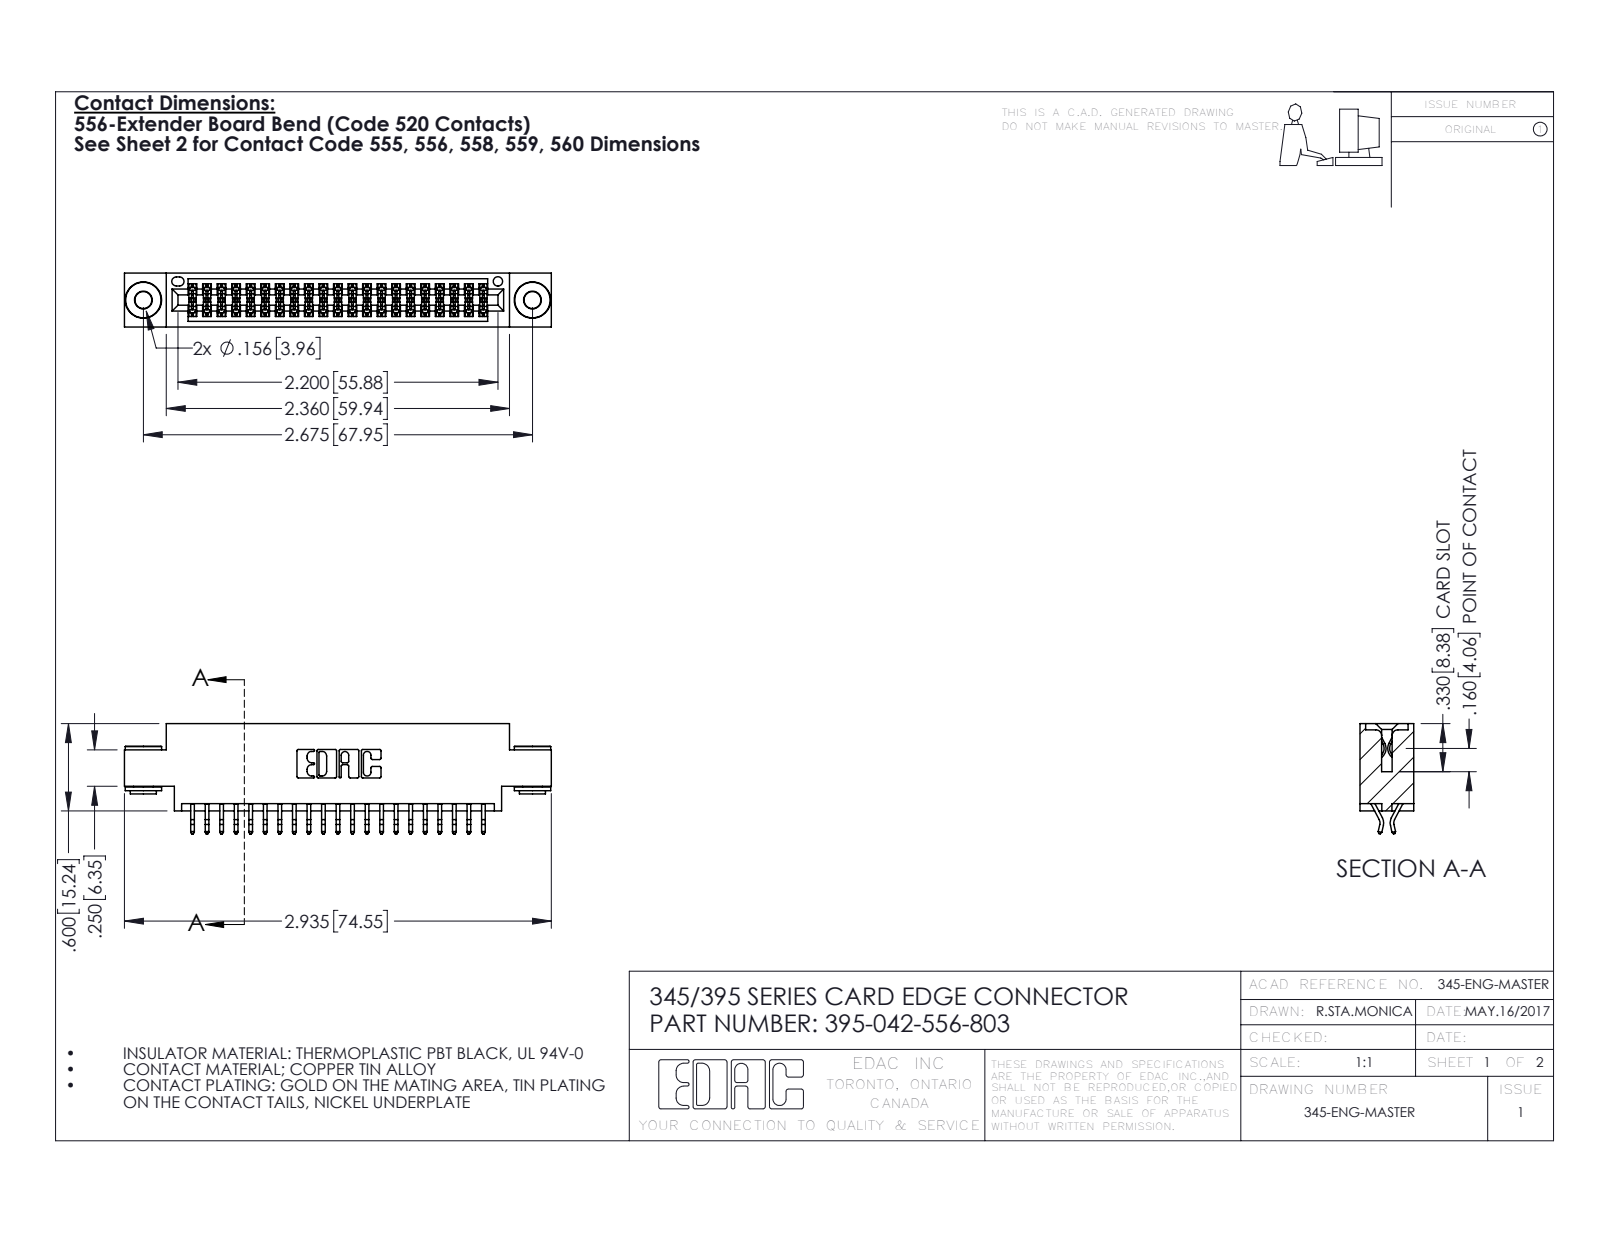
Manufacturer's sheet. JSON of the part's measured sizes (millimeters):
{"part_name": "345-292-001_556 Tail; 345 Part_0.170 Offset - 0.156 Dia-TH; 395-042-556-803; 345-250-002_345-250-002-102", "step_written_by": "SolidWorks 2016 (CONFIG_CONTROL_DESIGN)", "units": "millimeters", "bodies": {"solids": 45, "faces": 2520, "planar": 1648, "cylindrical": 864, "other": 8}, "overall_size": [74.5, 19.2, 9.4], "volume_mm3": 6950, "surface_area_mm2": 10180, "round_holes": [[2.9, 2], [4, 2], [1.6, 1]], "round_bosses_or_shafts": [[6.4, 2], [4.6, 2], [3.5, 2]], "partial_cylinders_radius": [[0.2, 63], [0.3, 22], [0.2, 6], [0.8, 6], [0.7, 3], [0.3, 2], [0.4, 2], [0.5, 2]], "face_to_face_distances": [1.8, 7.6, 9.4, 5.1, 0.6, 2.5, 6.9, 5.7, 4.4, 2.5], "hole_center_spacings": [6.9, 62, 67.9]}
